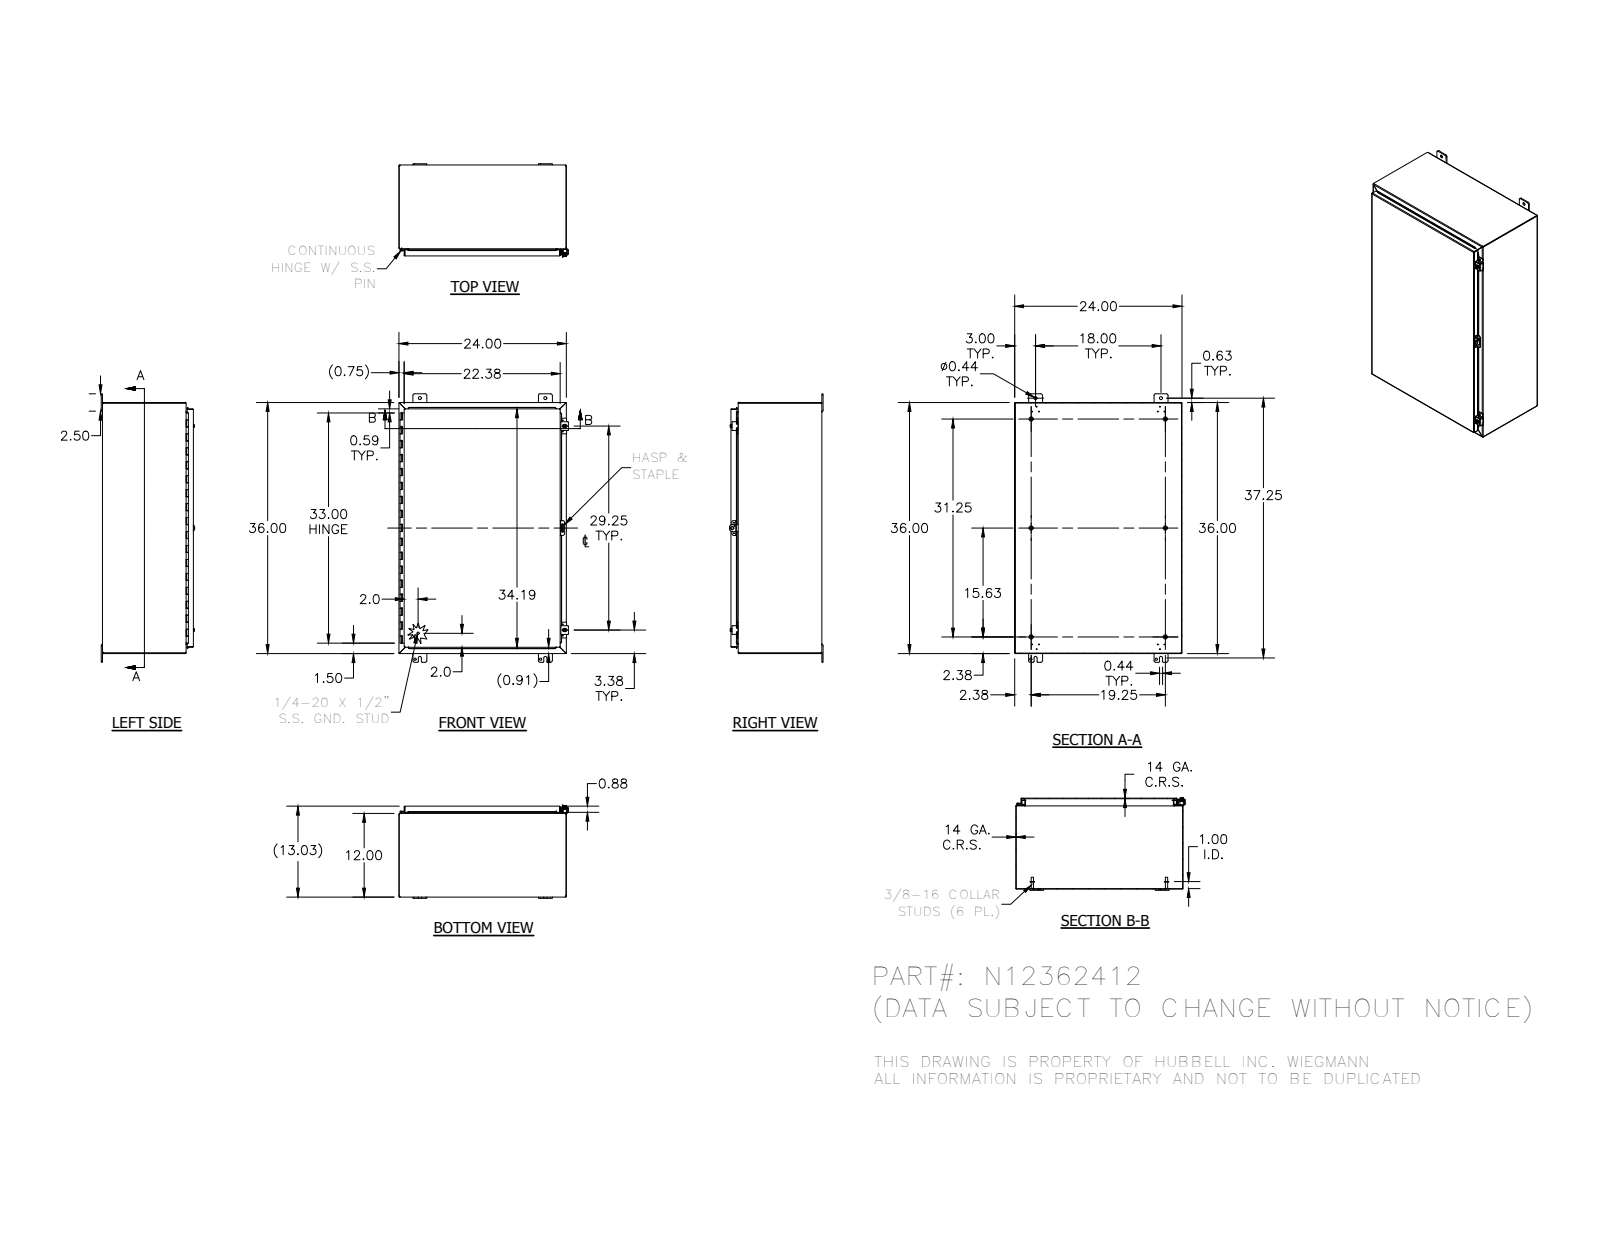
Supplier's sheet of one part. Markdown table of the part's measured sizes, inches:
| quantity | value |
| --- | --- |
| part name | N12362412; 34840; 38420; N12362412BKP (+8 more) |
| STEP written by | Autodesk Inventor 2012 (AUTOMOTIVE_DESIGN) |
| units | inches |
| bodies | 29 solids, 1100 faces (607 planar, 374 cylindrical, 119 other) |
| overall size | 38.5 × 24.311 × 13.41 |
| volume | 274.3 in³ |
| surface area | 7 231 in² |
| round holes (diameter × count) | 0.12 × 12, 0.11 × 7, 0.313 × 4, 0.438 × 4, 0.211 × 2, 0.281 × 2, 0.3 × 2, 0.125 × 1, 0.156 × 1, 0.5 × 1 |
| round bosses / shafts (diameter × count) | 0.625 × 6, 0.33 × 6, 0.25 × 4, 0.52 × 2, 0.5 × 2, 0.35 × 2, 0.115 × 2, 0.337 × 1 |
| partial cylindrical surfaces (radius × count) | 0.03 × 27, 0.063 × 25, 0.125 × 25, 0.25 × 25, 0.031 × 23, 0.105 × 23, 0.07 × 8, 0.1 × 4 |
| main face-to-face distances | 0.074, 12.959, 23.926, 12.885, 13.033, 35.926, 23.852, 24, 11.926, 1.033 |
| hole center spacings | 18, 0.759, 0.839, 0.94, 0.969, 1.593, 1.995, 17.37 |
